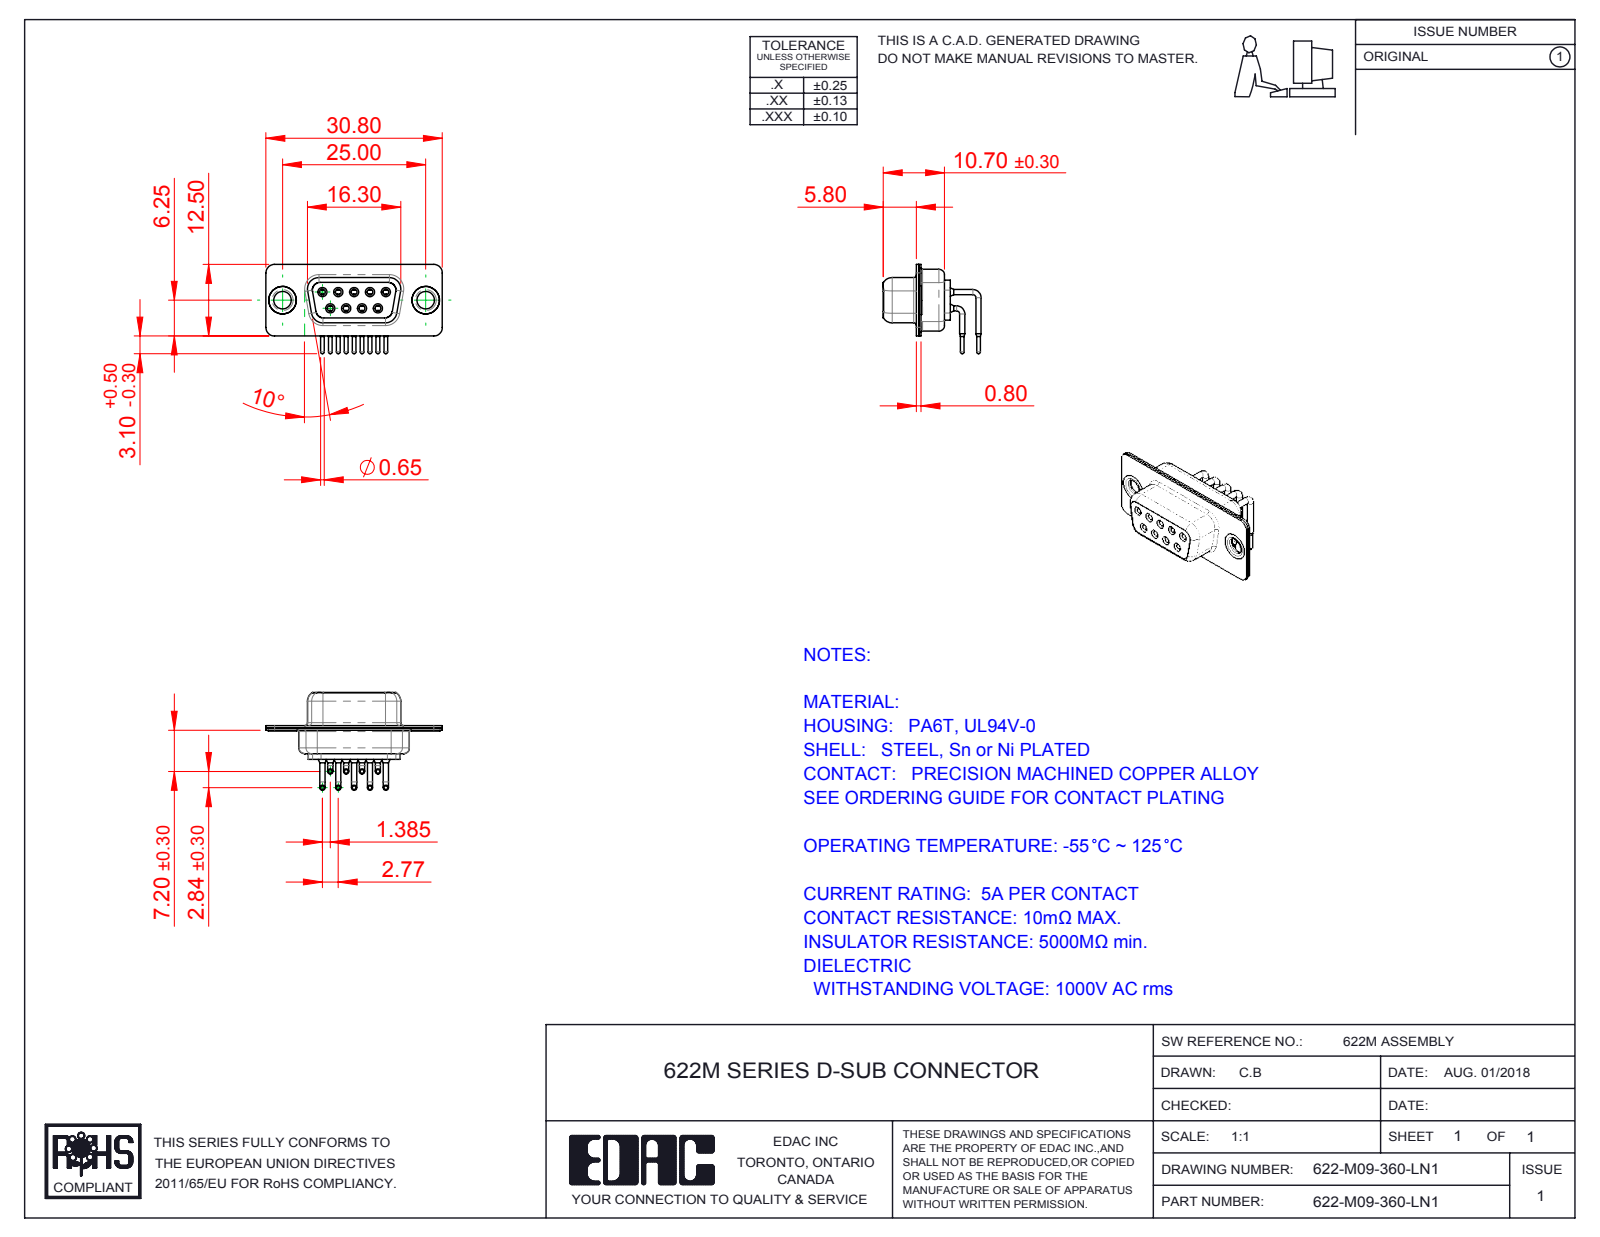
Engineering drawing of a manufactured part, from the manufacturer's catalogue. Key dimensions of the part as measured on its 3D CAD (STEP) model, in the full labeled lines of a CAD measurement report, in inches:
Part name (STEP PRODUCT): 622M Contact Row 2; 622M Shell Front_09 Contacts; 622M Shell Rear_09 Contacts; 622M Thru Hole Rivet (+3 more)
STEP written by: SolidWorks 2016 (CONFIG_CONTROL_DESIGN)
Units: inches
Bodies: 14 solids, 730 faces (202 planar, 328 cylindrical, 200 other)
Overall size (bounding box): 1.213 × 0.673 × 0.614
Volume: 0.102 in³ · Surface area: 6.834 in²
Round holes (diameter × count): ⌀0.039 ×9, ⌀0.043 ×9, ⌀0.067 ×9, ⌀0.071 ×9, ⌀0.079 ×9, ⌀0.12 ×2, ⌀0.157 ×2, ⌀0.189 ×2
Round bosses / shafts (diameter × count): ⌀0.035 ×18, ⌀0.063 ×9, ⌀0.059 ×9, ⌀0.026 ×9, ⌀0.197 ×2, ⌀0.193 ×2, ⌀0.14 ×2
Partial cylindrical surfaces — rounded edges, fillets, slot ends (radius × count): R0.059 ×16, R0.079 ×12, R0.053 ×8, R0.063 ×8, R0.01 ×4, R0.02 ×4, R0.024 ×4, R0.026 ×4
Main face-to-face distances: 0.016, 0.031, 0.057, 0.352, 0.091, 0.244, 0.335, 0.075, 0.033, 0.368
Hole centre spacings: 0.124, 0.109, 0.218, 0.198, 0.198, 0.327, 0.28, 0.294
